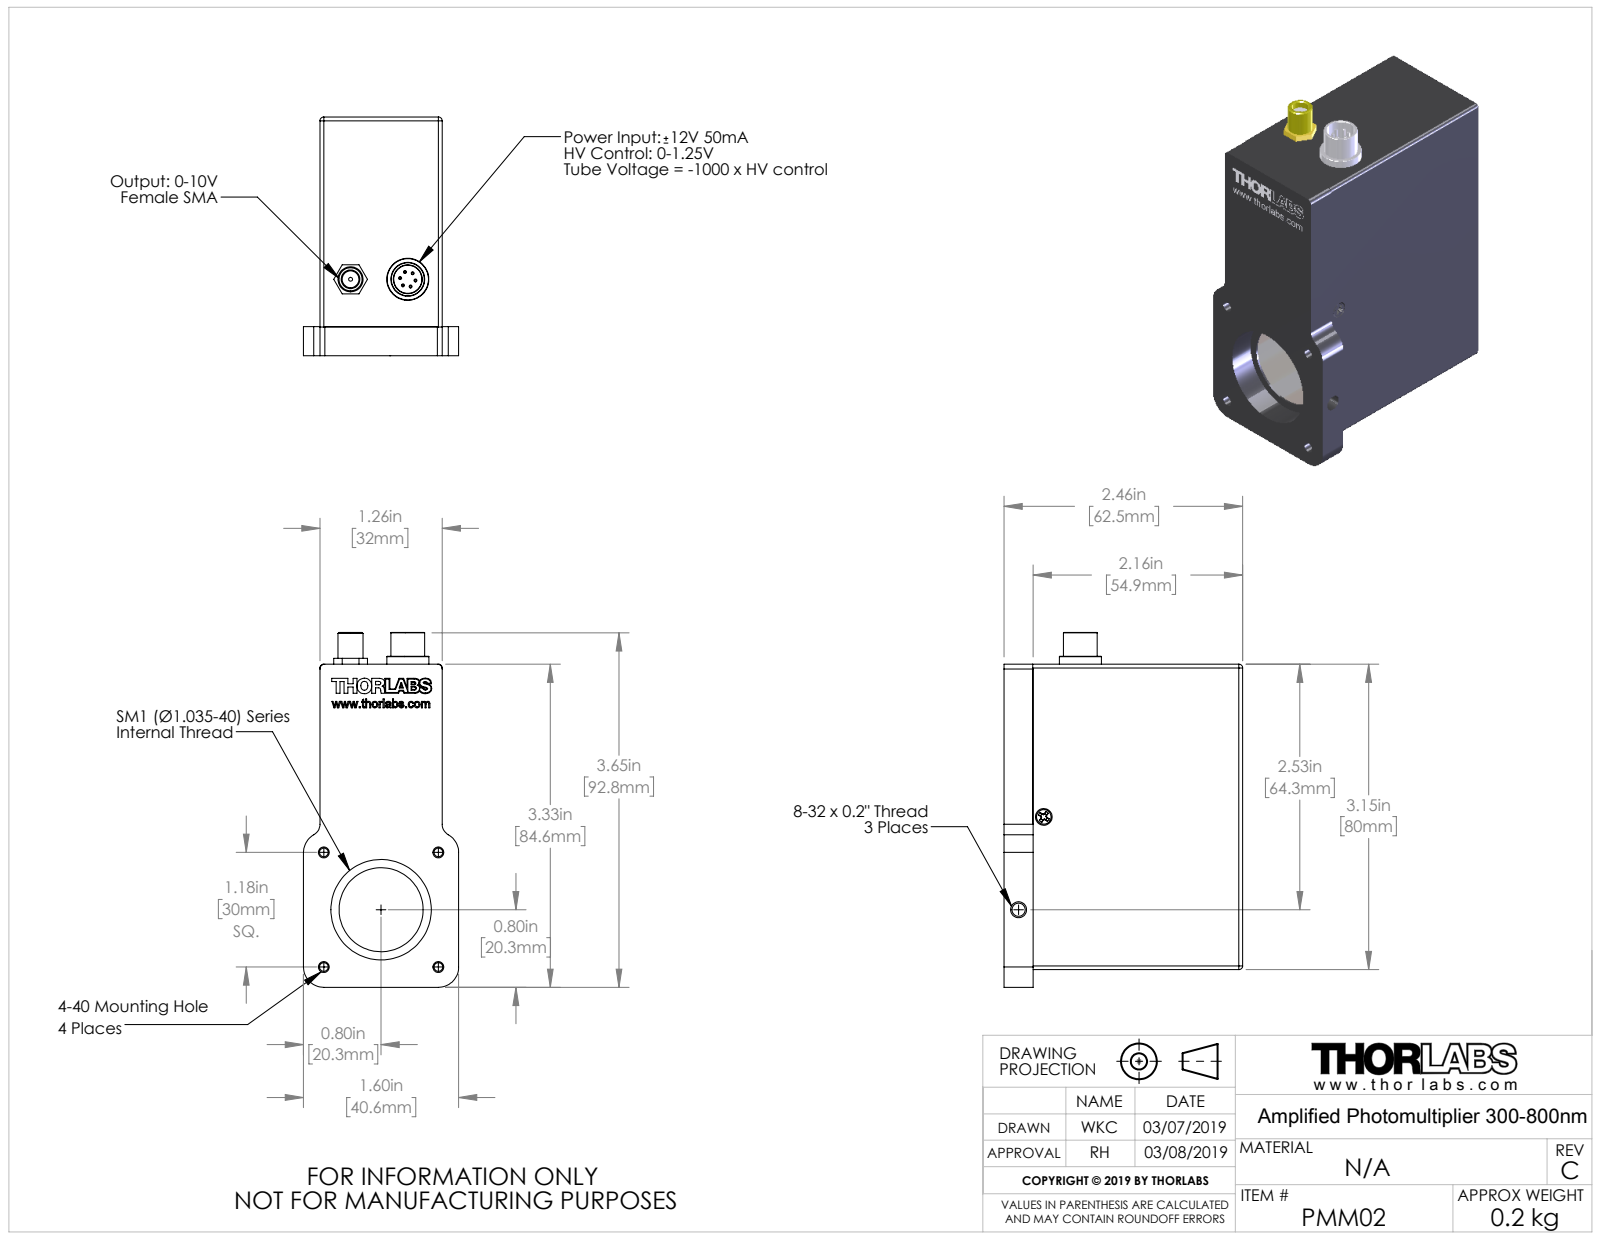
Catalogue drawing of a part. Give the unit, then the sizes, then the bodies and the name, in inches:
Units: inches
Overall size (bounding box): 3.658 × 2.46 × 1.6
Round holes (diameter × count): ⌀0.112 ×4, ⌀0.164 ×2, ⌀0.04 ×1, ⌀0.086 ×1, ⌀0.173 ×1, ⌀0.29 ×1, ⌀0.866 ×1, ⌀1.035 ×1, ⌀1.12 ×1
Round bosses / shafts (diameter × count): ⌀0.03 ×6, ⌀0.433 ×1, ⌀0.348 ×1, ⌀0.258 ×1, ⌀0.15 ×1, ⌀0.058 ×1
Partial cylindrical surfaces — rounded edges, fillets, slot ends (radius × count): R0.039 ×8, R0.209 ×4, R0.05 ×2, R0.125 ×2
Main face-to-face distances: 1.26, 2.461, 3.15, 0.045, 1.215, 2.161, 0.3, 0.035, 2.126, 0.335
Hole centre spacings: 0.835, 1.181, 1.67, 0.591, 0.694, 0.711, 0.991
Bodies: 0 solids, 241 faces (102 planar, 83 cylindrical, 56 other)
Part name (STEP PRODUCT): 17495-E0W
STEP written by: SolidWorks 2016 (AUTOMOTIVE_DESIGN)
